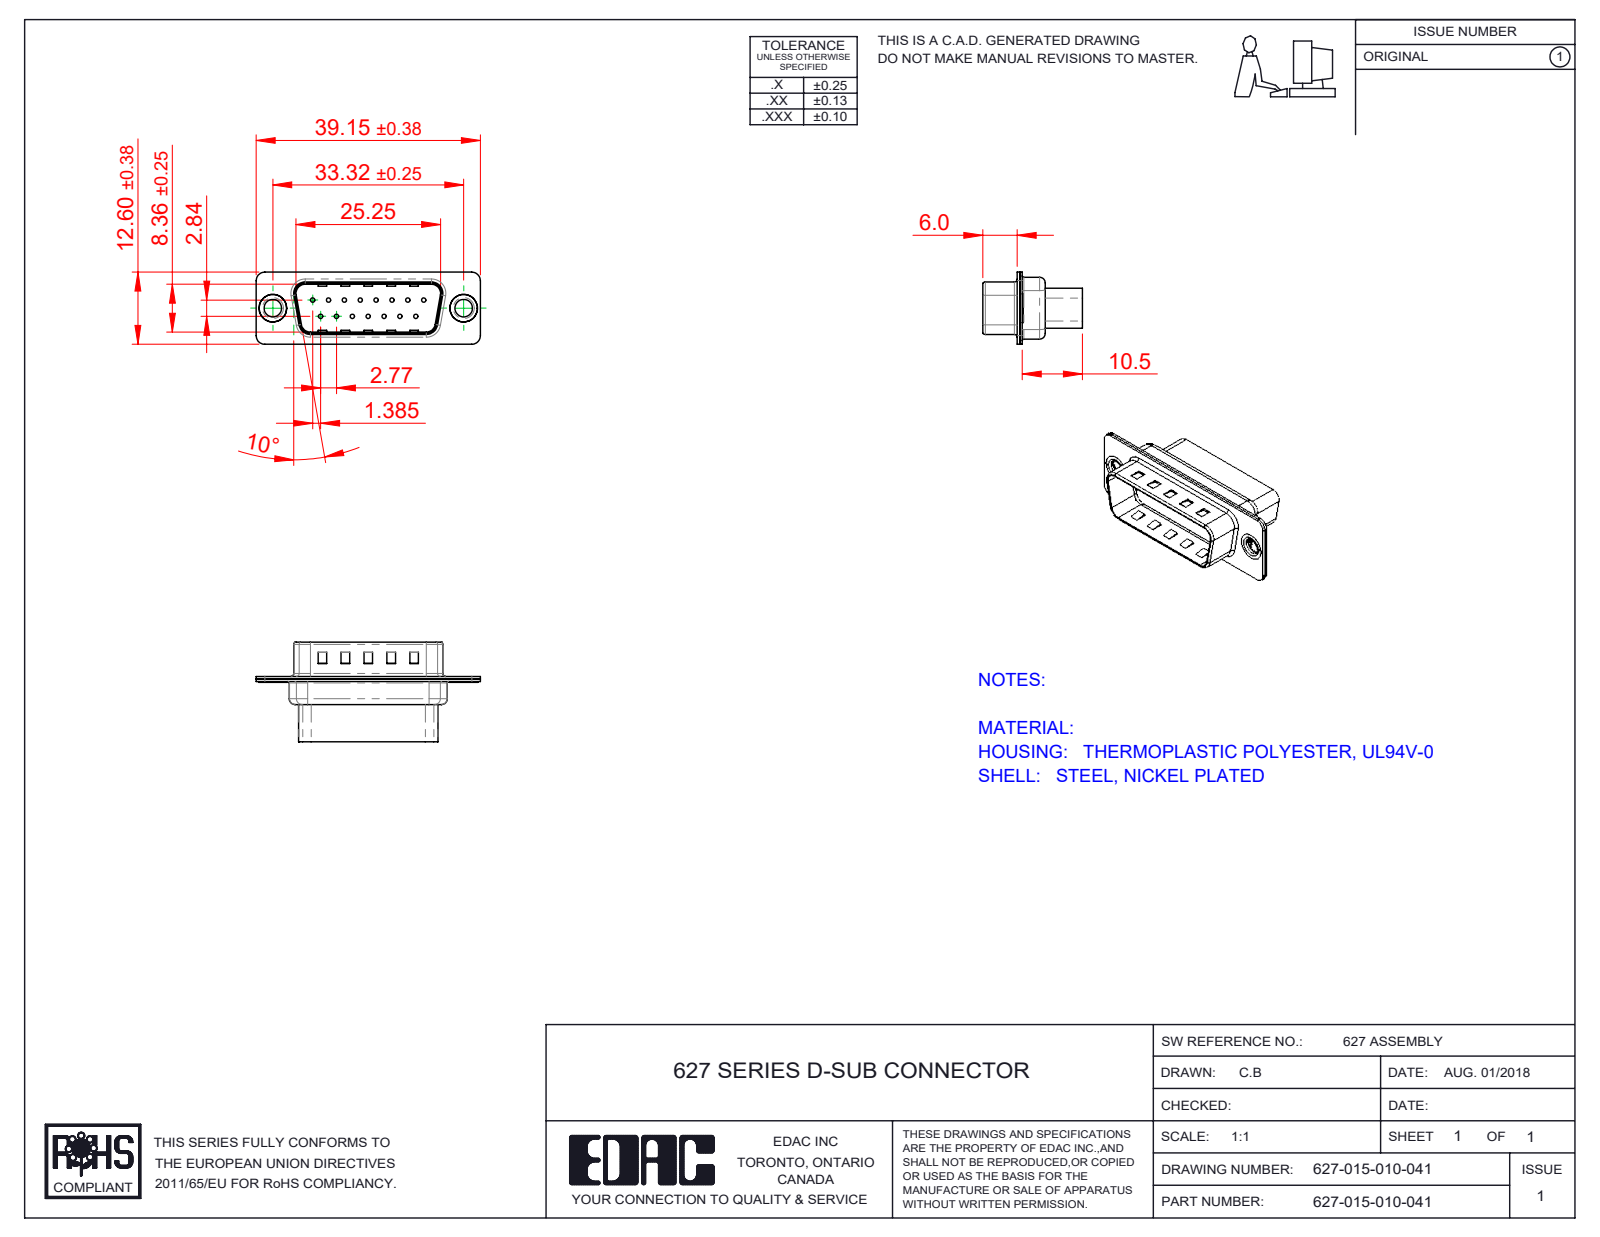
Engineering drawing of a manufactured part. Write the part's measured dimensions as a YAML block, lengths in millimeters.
part_name: "627 Housing_15 HP; 627-015-010-241; 627 Shell Rear_15 Contacts; 627 Thru Hole Rivet (+1 more)"
step_written_by: "SolidWorks 2020 (CONFIG_CONTROL_DESIGN)"
units: millimeters
bodies: {solids: 5, faces: 434, planar: 169, cylindrical: 207, other: 58}
overall_size: [39.15, 17.4, 12.6]
volume: 2286
surface_area: 4571
round_holes:
  - {diameter: 0.75, count: 15}
  - {diameter: 1.6, count: 15}
  - {diameter: 2, count: 15}
  - {diameter: 3.05, count: 2}
  - {diameter: 4, count: 2}
  - {diameter: 4.8, count: 2}
round_bosses_or_shafts:
  - {diameter: 5, count: 2}
  - {diameter: 4.9, count: 2}
  - {diameter: 3.55, count: 2}
partial_cylinders:
  - {radius: 1.5, count: 16}
  - {radius: 2, count: 12}
  - {radius: 0.5, count: 8}
  - {radius: 1.6, count: 8}
  - {radius: 0.25, count: 4}
  - {radius: 0.6, count: 4}
  - {radius: 0.65, count: 4}
  - {radius: 0.9, count: 4}
face_to_face_distances: [0.4, 0.45, 0.9, 0.82, 9.58, 0.68, 7.68, 1.08, 8.08, 8.76]
hole_center_spacings: [3.16, 2.77, 5.54, 8.31, 11.08, 5.03, 5.04, 7.48]
